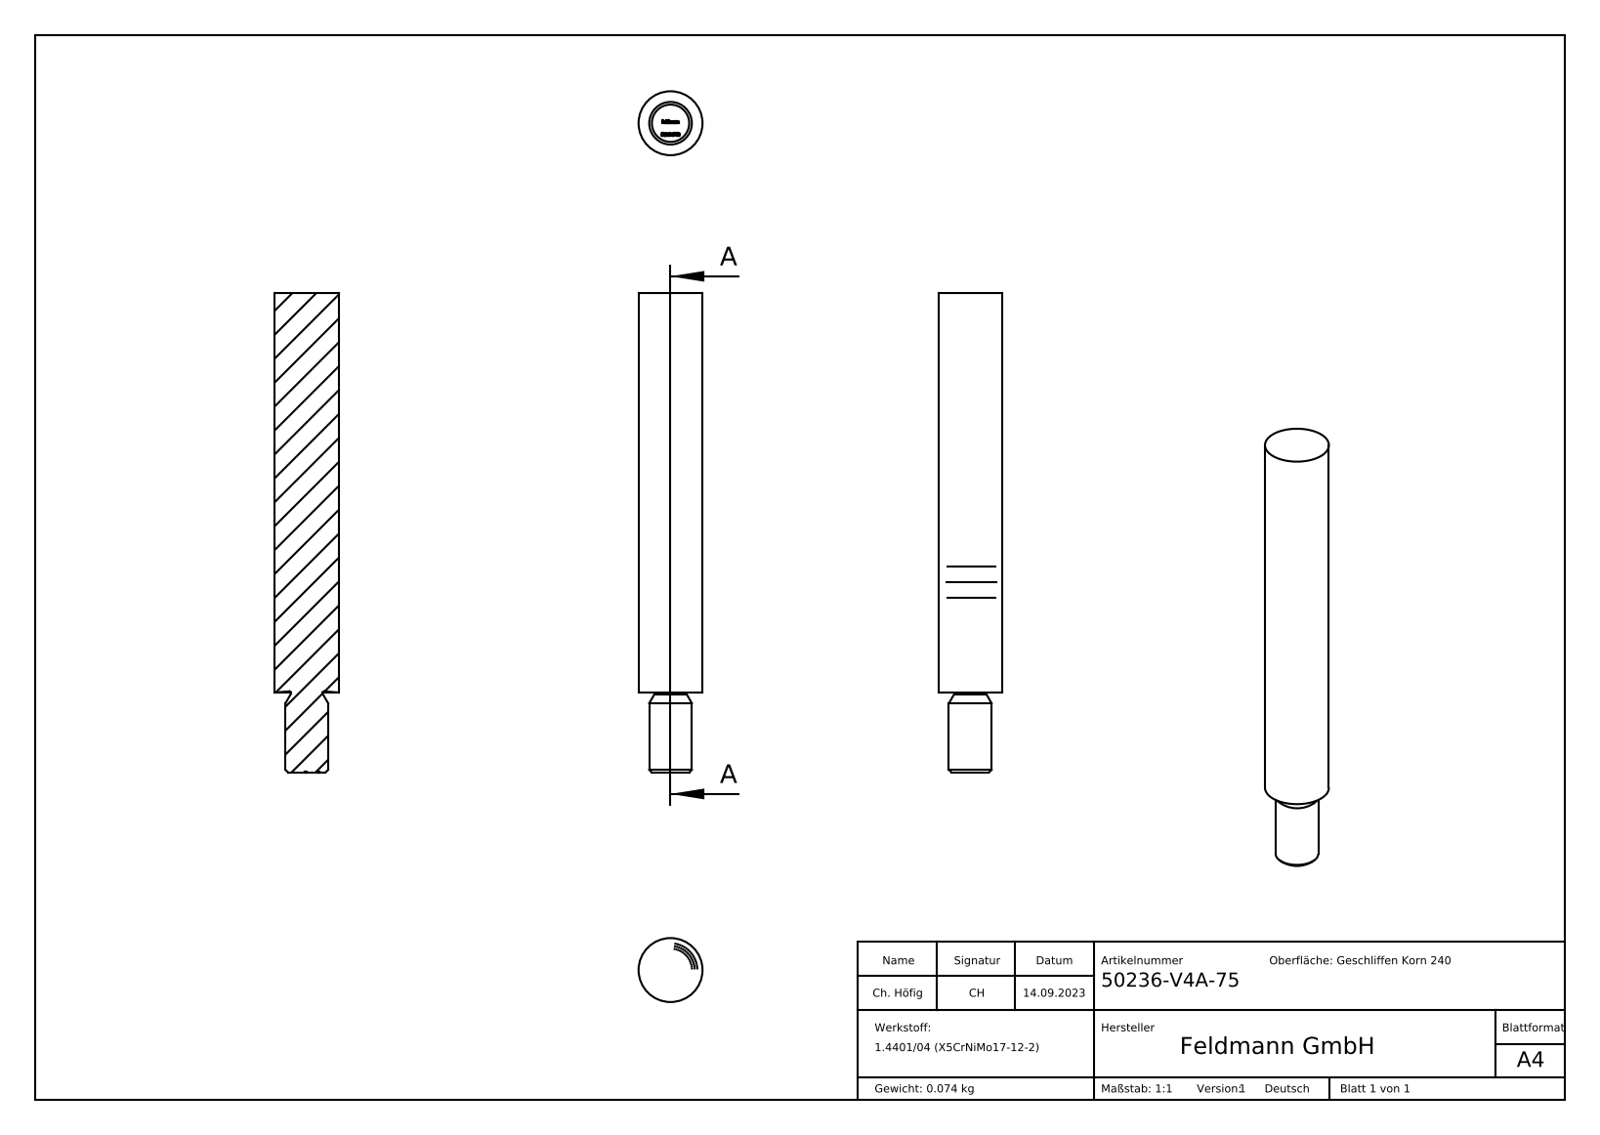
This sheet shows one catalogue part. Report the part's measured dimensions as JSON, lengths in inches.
{"part_name": "50236-V4A-75", "step_written_by": "SolidWorks 2018 (CONFIG_CONTROL_DESIGN)", "units": "inches", "bodies": {"solids": 1, "faces": 266, "planar": 157, "cylindrical": 2, "other": 107}, "overall_size": [3.543, 0.472, 0.472], "volume_in3": 0.561, "surface_area_in2": 5.349, "round_bosses_or_shafts": [[0.472, 1], [0.315, 1]], "face_to_face_distances": [3.543, 3.539, 0.03, 0.051, 0.094, 0.094, 0.028, 0.061, 0.096, 0.022]}
